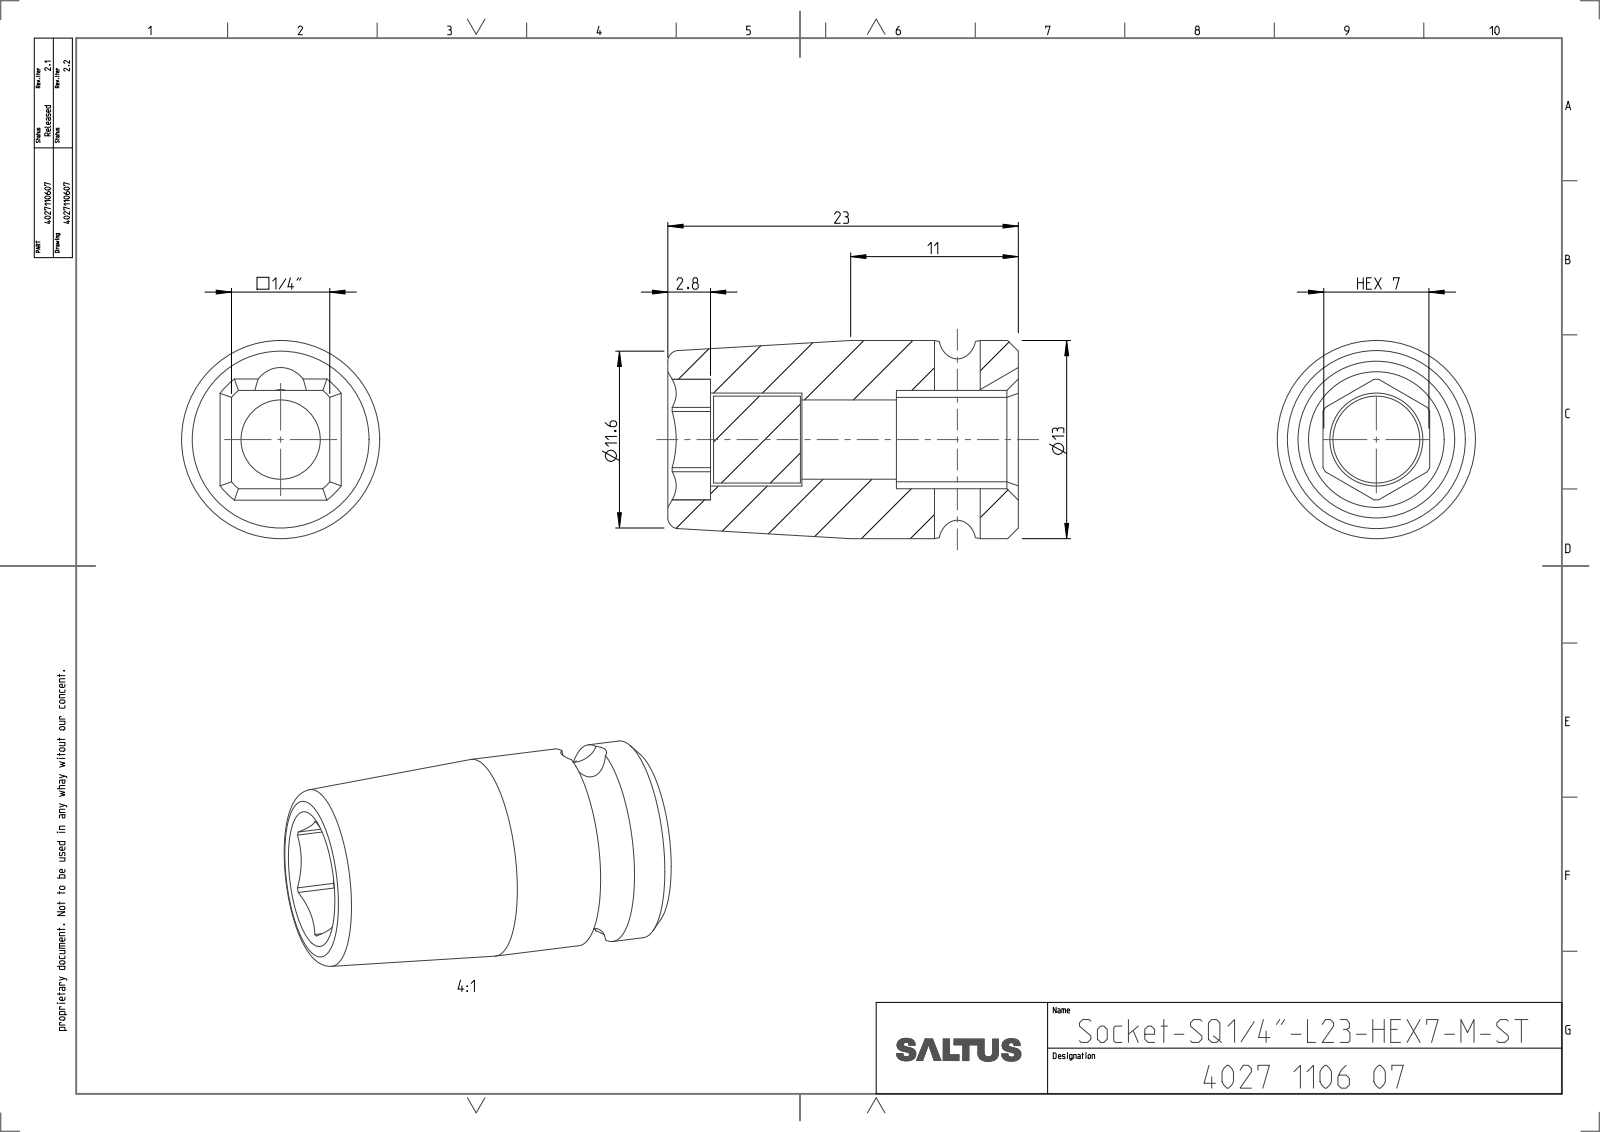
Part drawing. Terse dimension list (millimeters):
name: 4027110607
written by: CREO PARAMETRIC BY PTC INC, 2022414 (CONFIG_CONTROL_DESIGN)
unit: mm
bodies: 2 solids, 61 faces (22 planar, 23 cylindrical, 16 other)
size: 23 × 13 × 13
volume: 2 274 mm³; area: 1 687 mm²
holes: 1× ⌀3, 1× ⌀6.1
bosses: 1× ⌀13, 1× ⌀5.7
rounds: 1× R2, 1× R3.96, 1× R4.25
face distances: 6.46, 8, 7, 14.3, 20, 6.3, 12, 5.7, 23, 15
